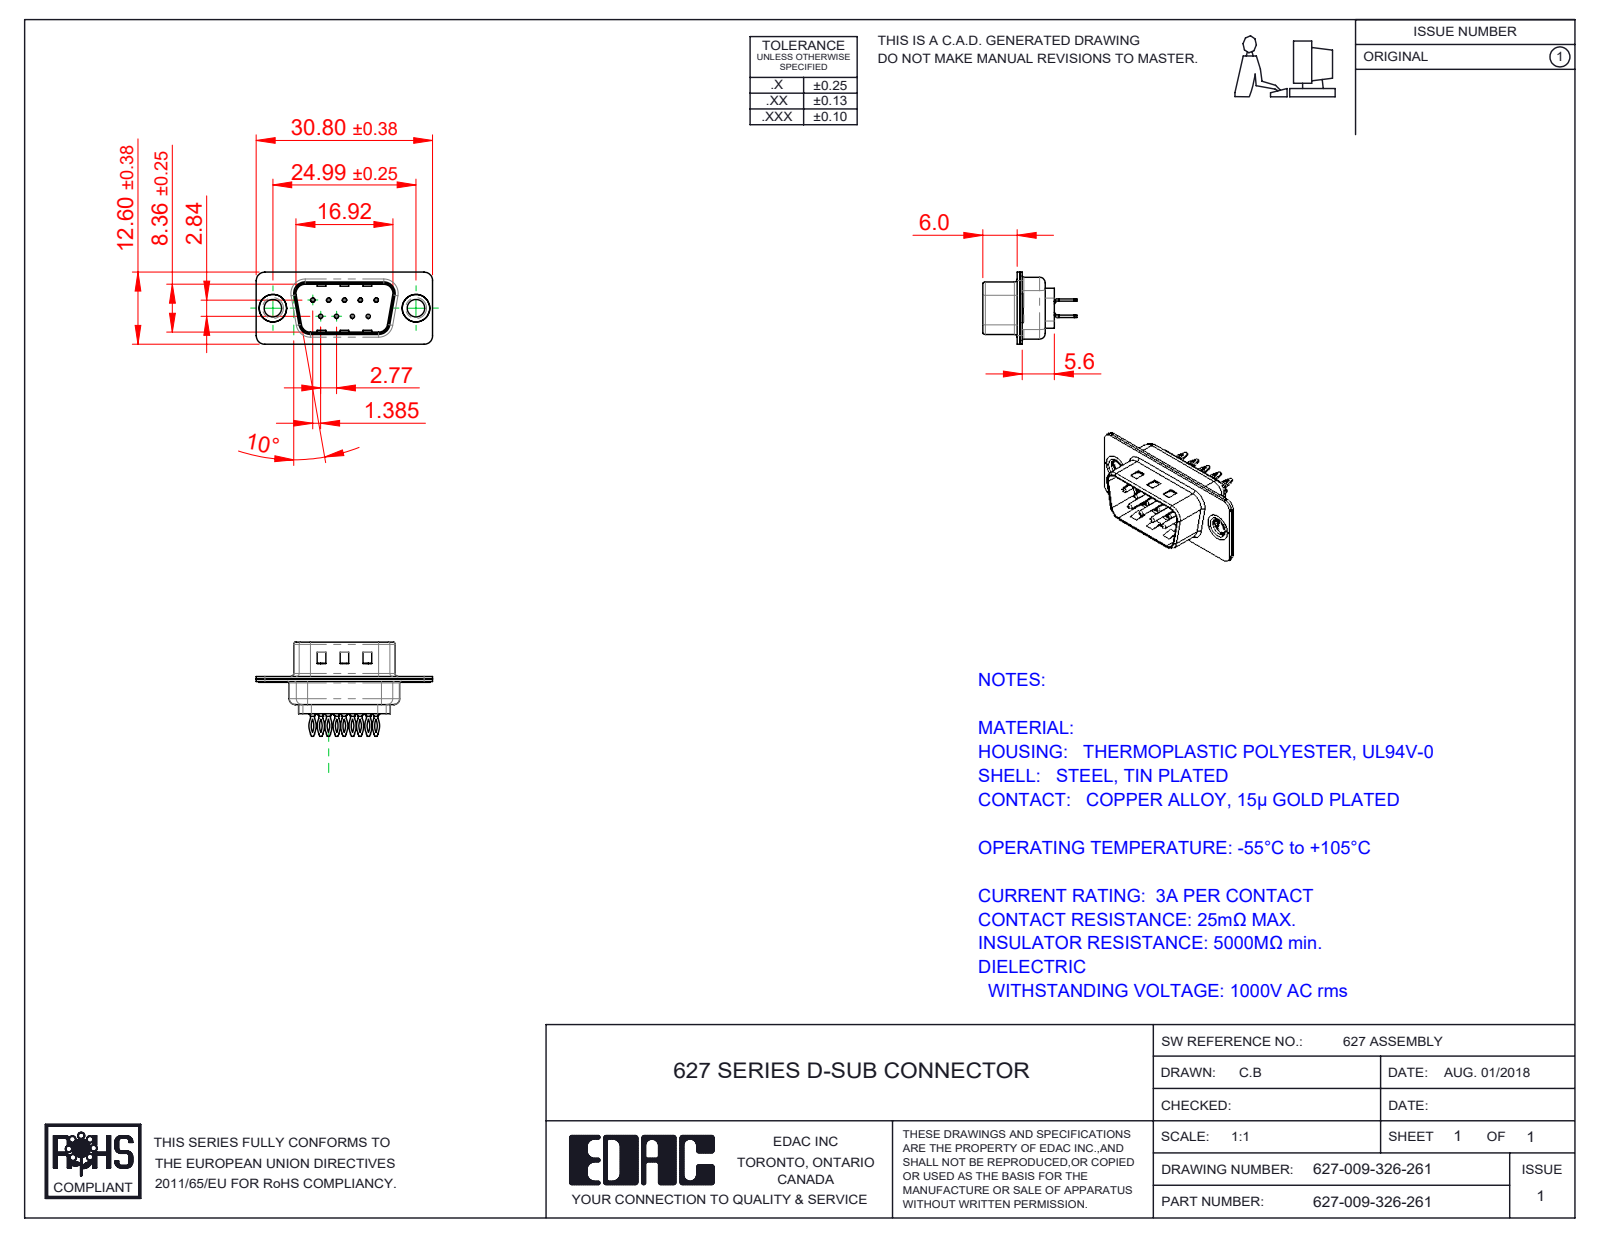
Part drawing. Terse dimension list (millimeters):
name: 627 Shell Front_09 Contacts; 627 Contact Row 2_26L; 627 Thru Hole Rivet; 627 Contact Row 1_26L (+3 more)
written by: SolidWorks 2020 (CONFIG_CONTROL_DESIGN)
unit: mm
bodies: 14 solids, 962 faces (287 planar, 392 cylindrical, 283 other)
size: 30.8 × 16.45 × 12.6
volume: 1 234 mm³; area: 3 761 mm²
holes: 9× ⌀0.35, 9× ⌀1.1, 9× ⌀1.6, 2× ⌀3.05, 2× ⌀4, 2× ⌀4.8
bosses: 9× ⌀2, 9× ⌀1.5, 9× ⌀0.75, 2× ⌀5, 2× ⌀4.9, 2× ⌀3.55
rounds: 18× R1.5, 18× R2.92, 18× R3.33, 12× R2, 8× R0.5, 8× R1.6, 4× R0.25, 4× R0.6
face distances: 0.4, 0.45, 0.9, 0.82, 9.58, 1.4, 0.5, 8.76, 1.5, 6.05
hole spacings: 3.16, 2.77, 5.54, 5.03, 5.04, 8.31, 7.48, 7.49
